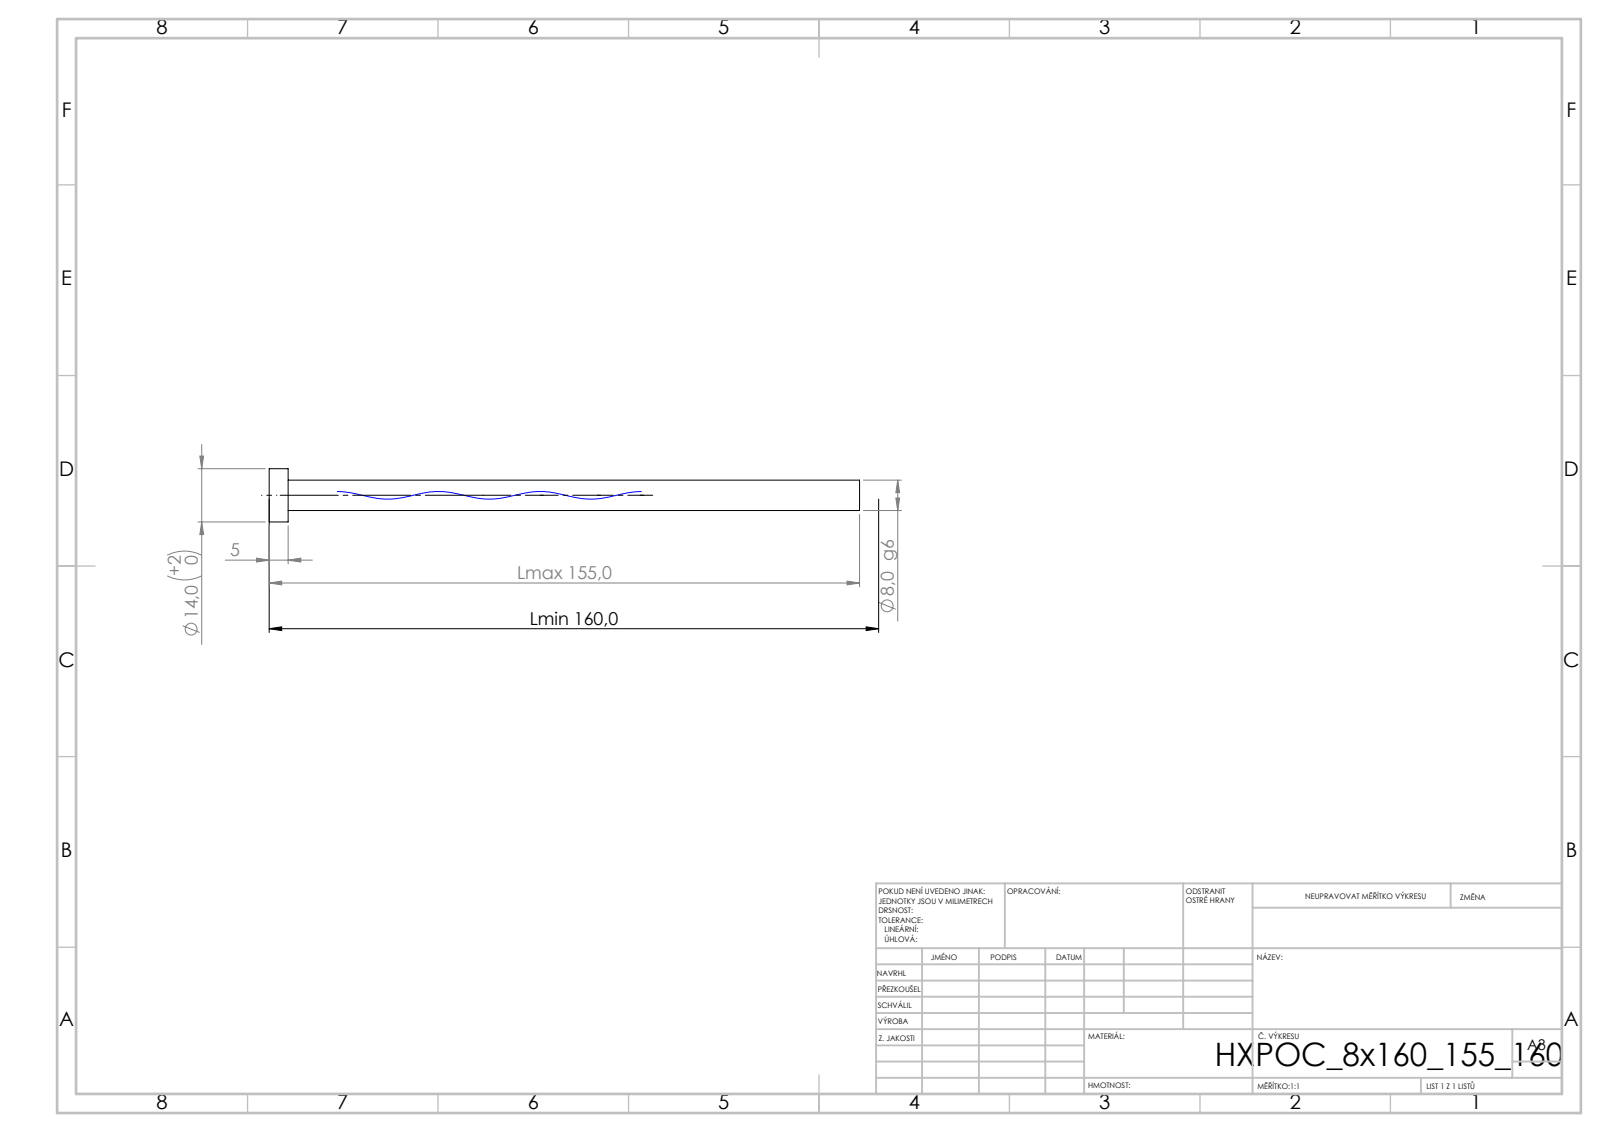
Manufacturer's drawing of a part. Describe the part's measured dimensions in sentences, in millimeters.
Its 3-D file was written by "SolidWorks 2019 (CONFIG_CONTROL_DESIGN)". It is 1 solid with 11 faces: 5 planar, 4 cylindrical and 2 other. Overall it measures 155 by 14 by 14 millimeters. Its volume is 8 308 cubic millimeters and its surface area 4 339 square millimeters. Round bosses or shafts: 1 of diameter 14, 1 of diameter 8. The main face-to-face distances are 5, 155, 150, 17.8, 97.8, 12.8, 92.8, 80, 137.2, 57.2.
